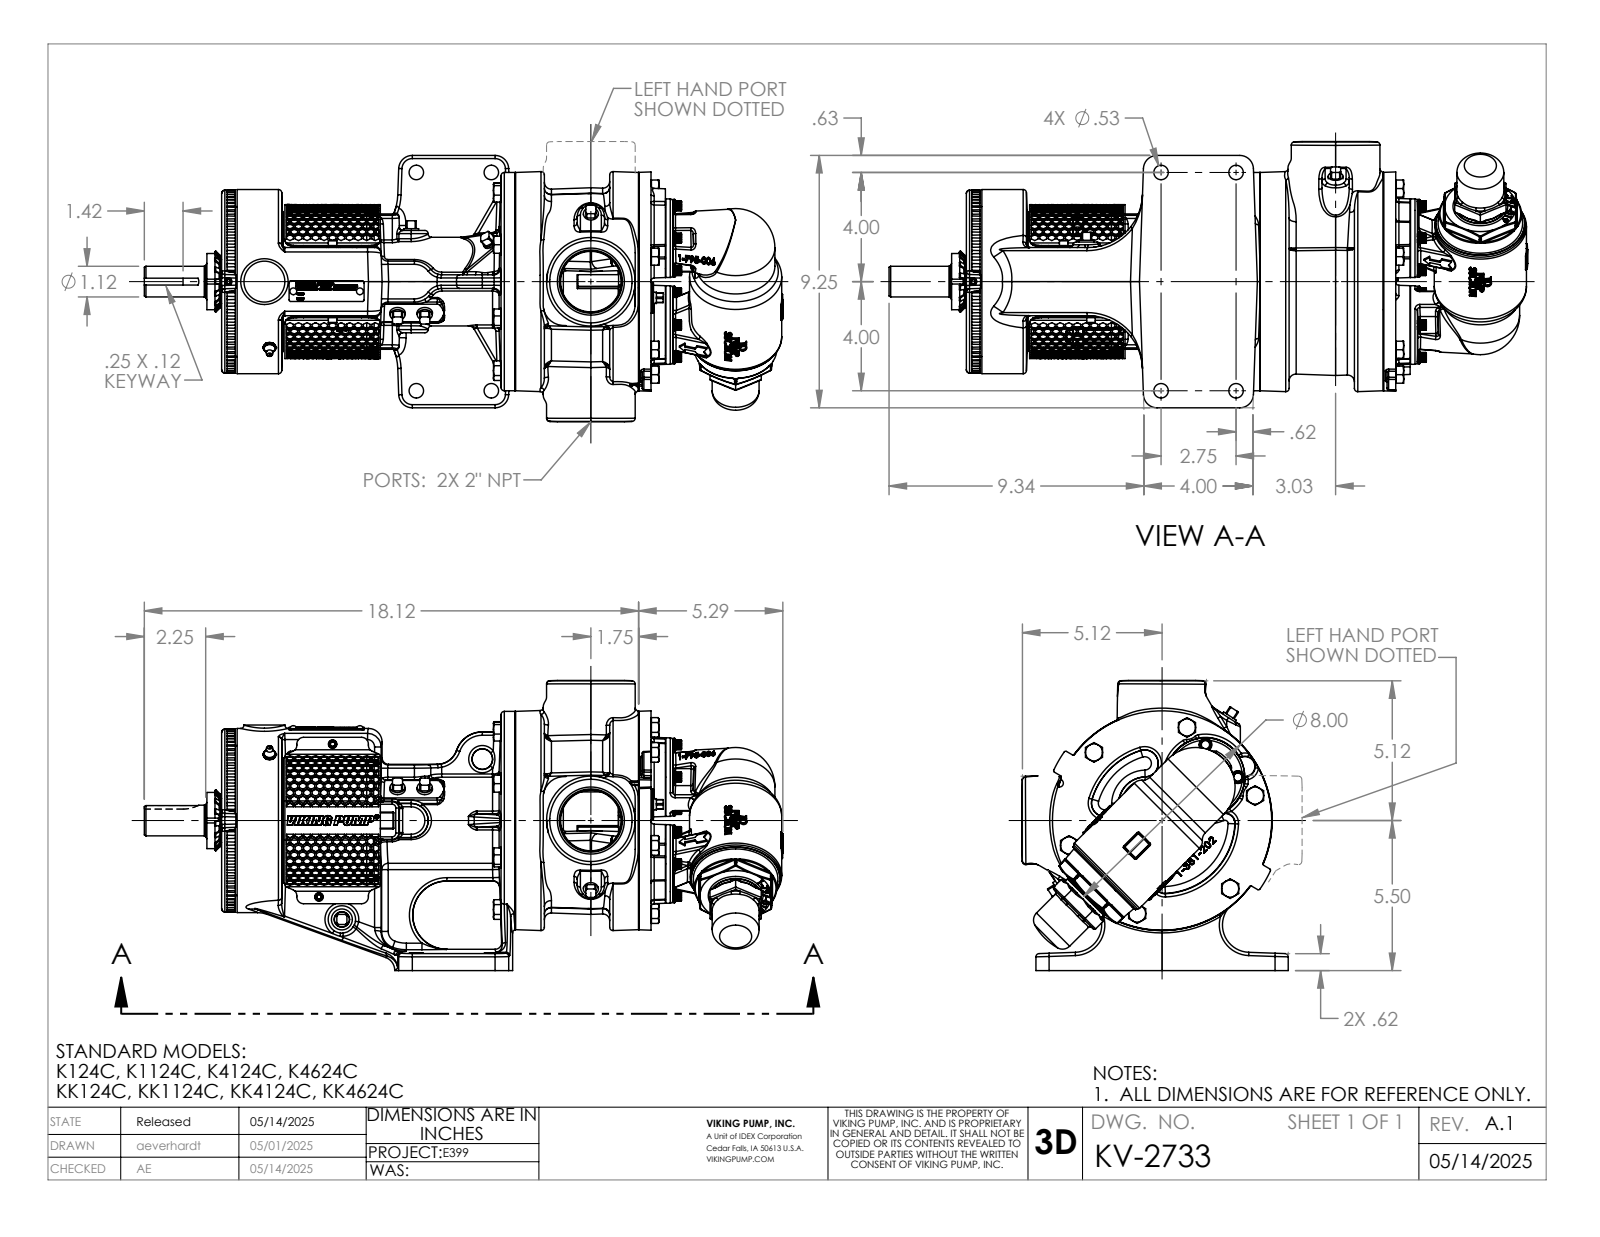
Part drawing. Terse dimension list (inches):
name: KV-2733
written by: SolidWorks 2024 (AUTOMOTIVE_DESIGN)
unit: in
bodies: 1 solid, 5118 faces (1746 planar, 718 cylindrical, 2654 other)
size: 23.412 × 10.634 × 9.759
volume: 532 in³; area: 1 010 in²
holes: 8× ⌀0.34, 8× ⌀0.344, 8× ⌀0.78, 6× ⌀0.197, 6× ⌀0.25, 4× ⌀0.531, 2× ⌀0.159, 2× ⌀0.313, 1× ⌀0.257, 1× ⌀0.453, 1× ⌀1.38, 1× ⌀1.387
bosses: 10× ⌀0.625, 8× ⌀0.469, 8× ⌀0.313, 5× ⌀2.88, 4× ⌀0.625, 3× ⌀0.437, 3× ⌀0.312, 2× ⌀3.25
rounds: 78× R0.12, 37× R0.03, 18× R0.24, 16× R0.12, 12× R0.5, 10× R0.25, 8× R0.09, 8× R0.178
face distances: 10.425, 0.5, 5.319, 15.744, 0.569, 4.75, 15.175, 0.069, 1, 1.5
hole spacings: 1.03, 3, 1.376, 2.385, 2.909, 3.531, 3.655, 3.799
